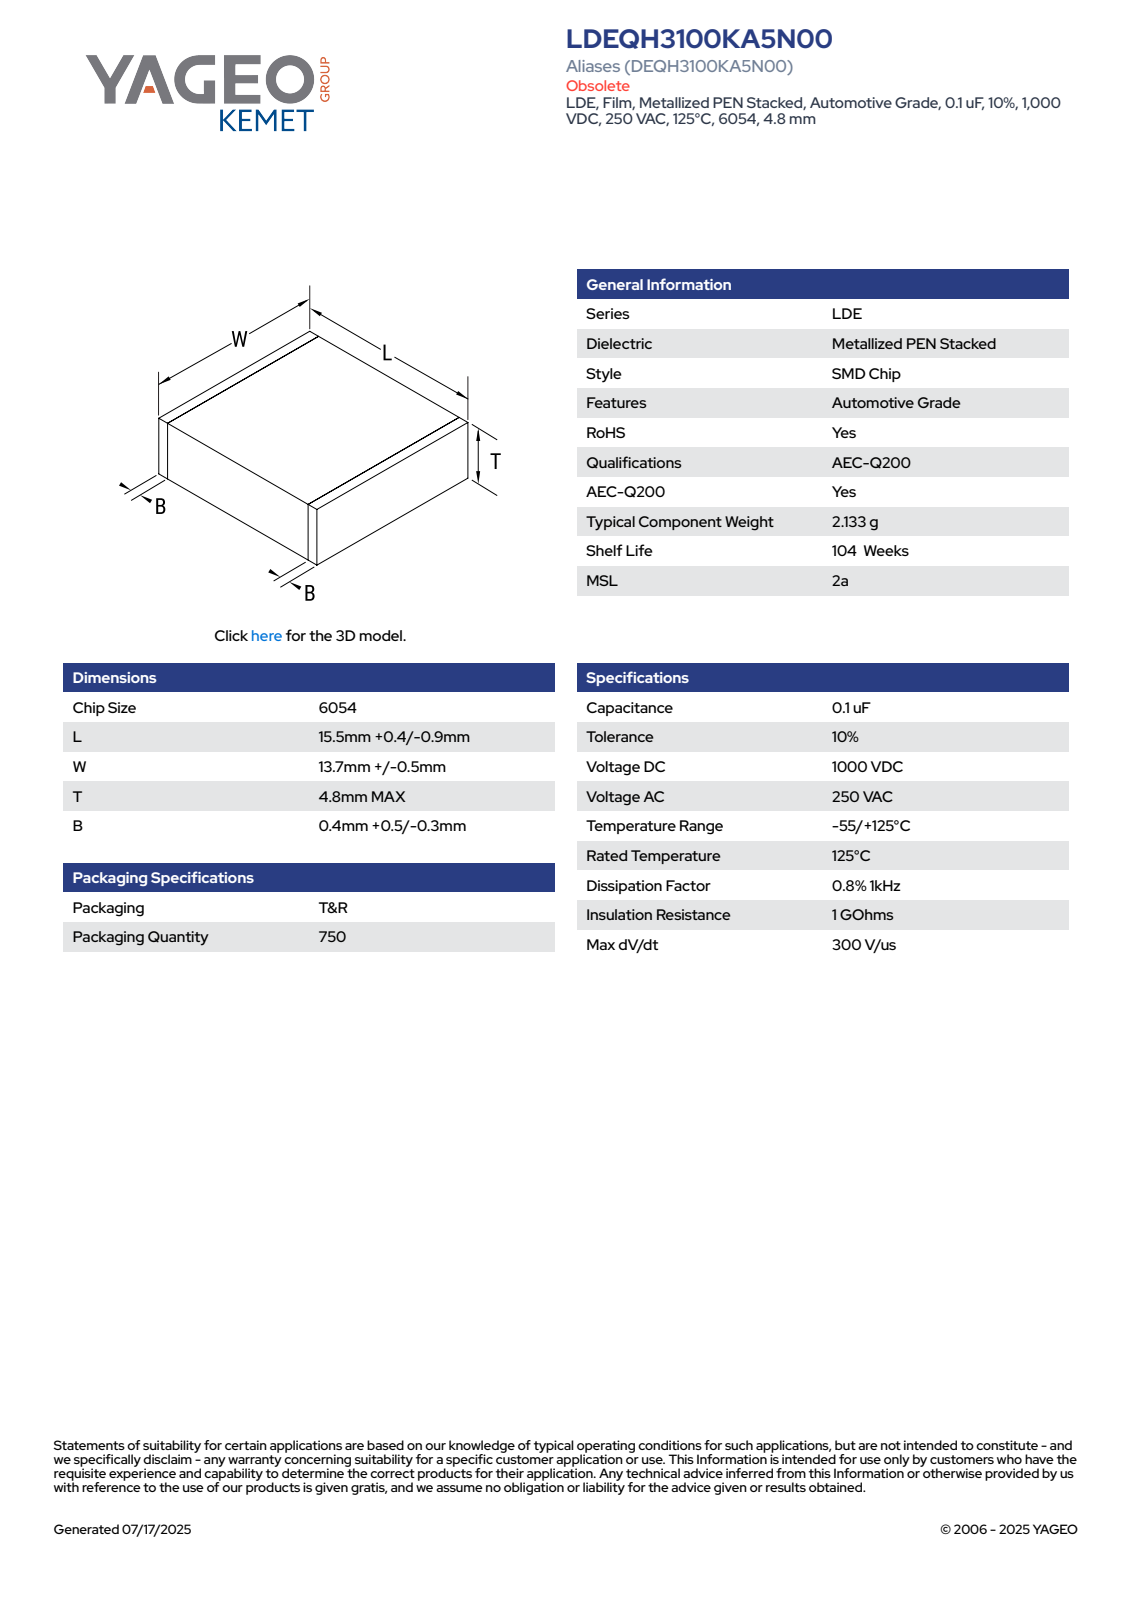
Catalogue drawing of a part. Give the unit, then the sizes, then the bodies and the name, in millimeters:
Units: millimetres
Overall size (bounding box): 15.9 × 14.2 × 4.8
Main face-to-face distances: 4.78, 14.18, 15.9, 4.79, 4.8, 14.19, 14.2, 0.5, 15.4, 14.9
Volume: 1 078 mm³ · Surface area: 752 mm²
Bodies: 4 solids, 73 faces (73 planar, 0 cylindrical, 0 other)
Part name (STEP PRODUCT): CFS_LDELDB_6054_L15.9W14.2T4.8B0.9
STEP written by: SolidWorks 2020 (AUTOMOTIVE_DESIGN)
